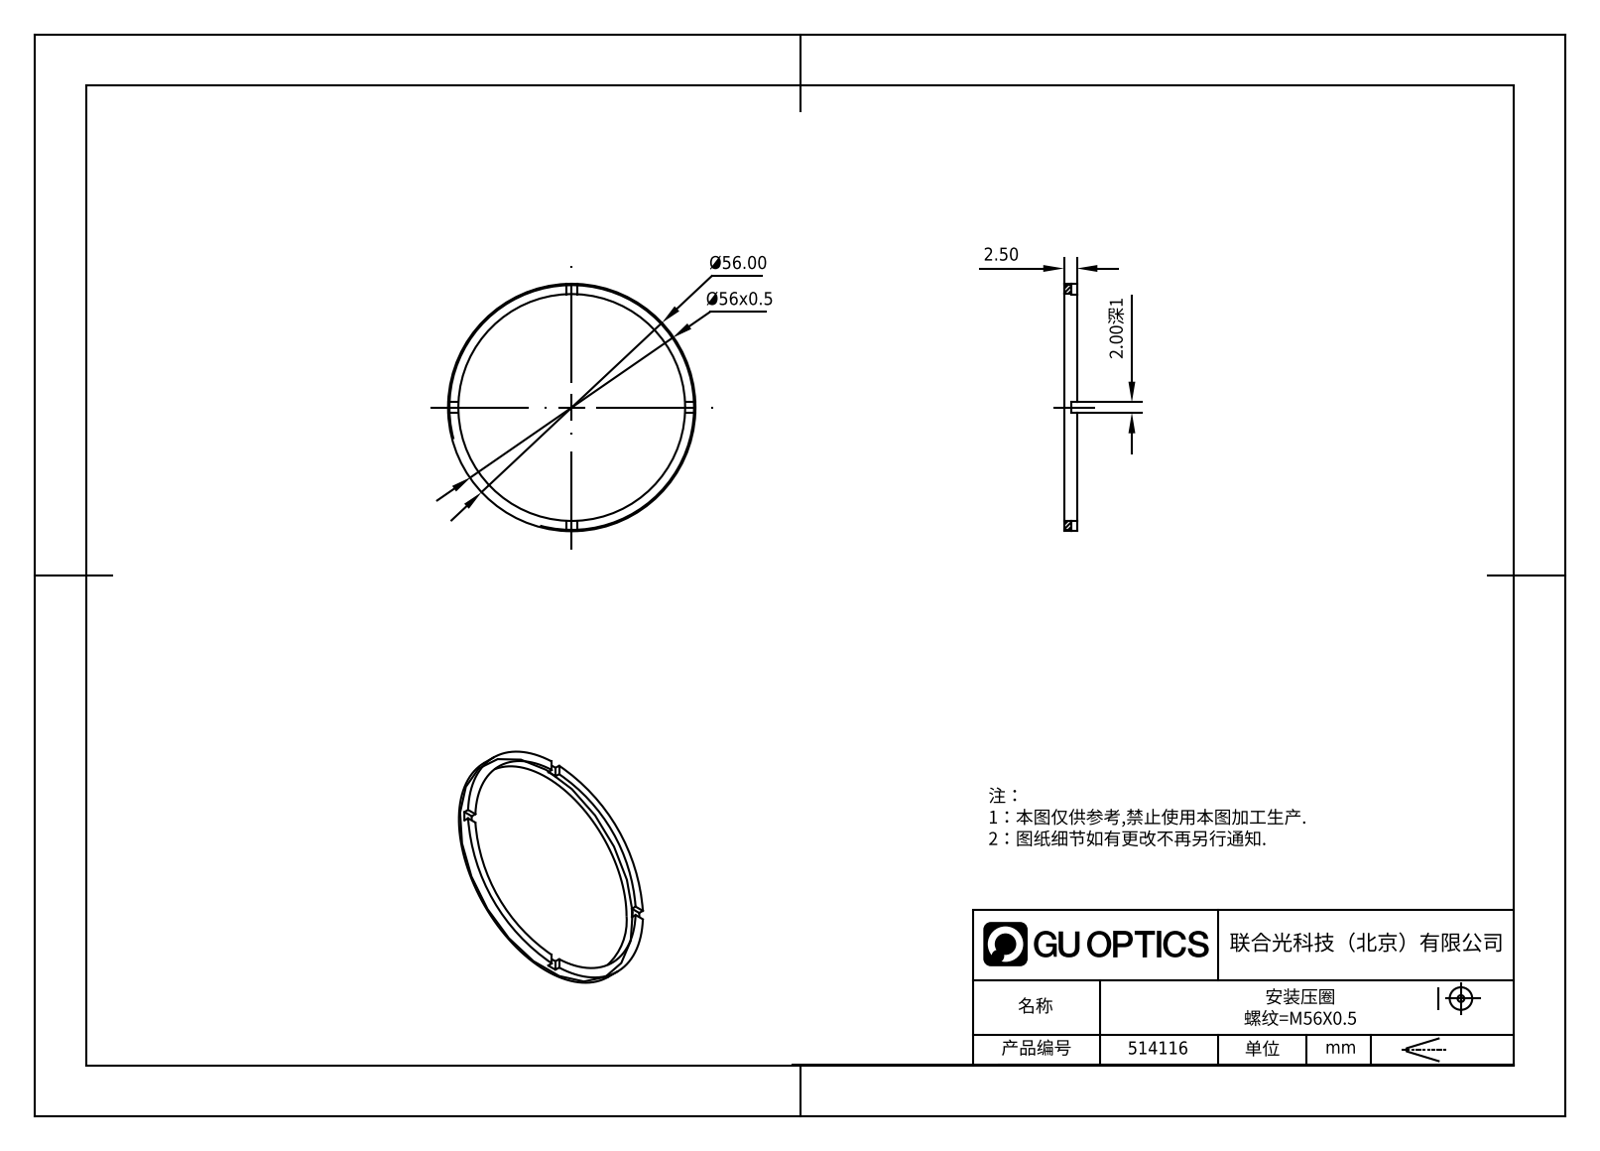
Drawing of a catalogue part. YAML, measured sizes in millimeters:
part_name: "514116"
step_written_by: "SolidWorks 2020 (CONFIG_CONTROL_DESIGN)"
units: millimeters
bodies: {solids: 1, faces: 21, planar: 17, cylindrical: 4, other: 0}
overall_size: [56, 56, 2.5]
volume: 1030
surface_area: 1685
round_holes:
  - {diameter: 51, count: 1}
round_bosses_or_shafts:
  - {diameter: 56, count: 1}
face_to_face_distances: [2.5, 1.5, 1, 2]
